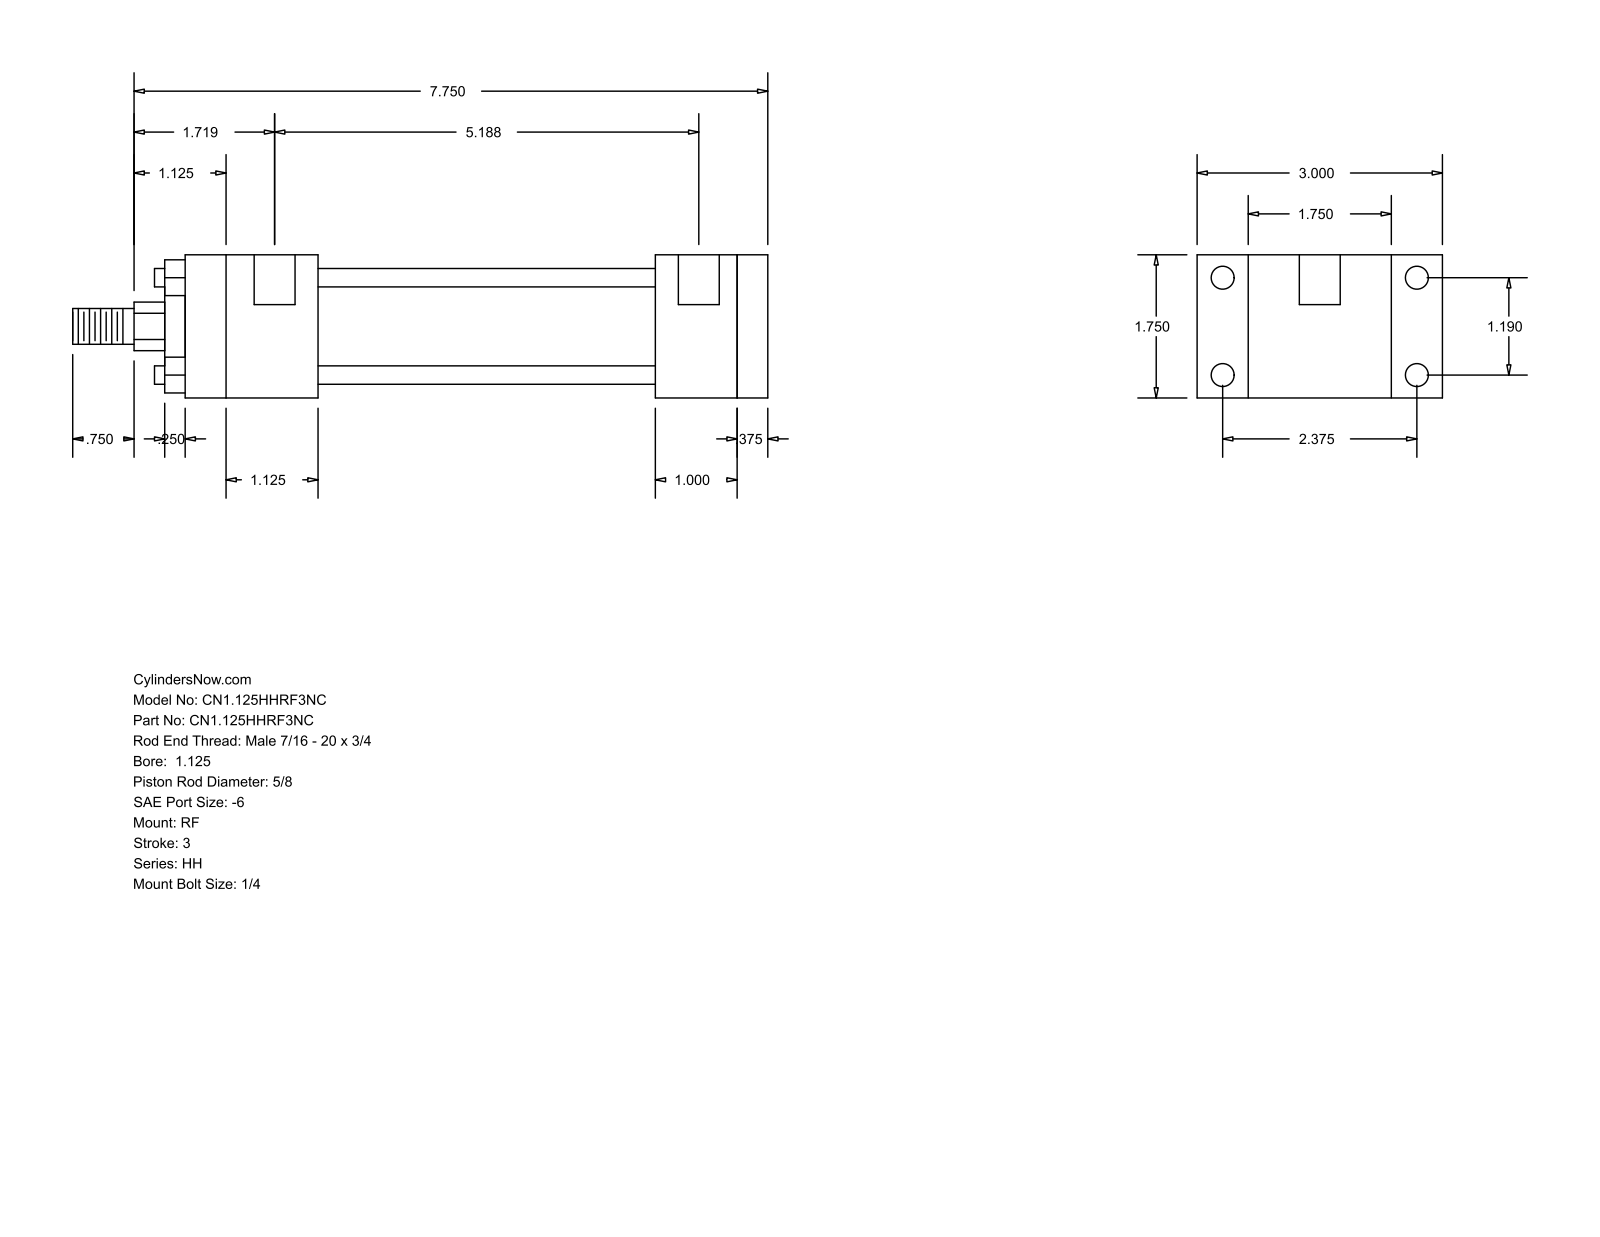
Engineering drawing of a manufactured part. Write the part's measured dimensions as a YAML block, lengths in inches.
part_name: "HH_RF__0112_0.625"
step_written_by: "GSSL Pune (CONFIG_CONTROL_DESIGN)"
units: inches
bodies: {solids: 0, faces: 92, planar: 64, cylindrical: 28, other: 0}
overall_size: [8.5, 3, 1.75]
round_holes:
  - {diameter: 0.219, count: 4}
  - {diameter: 0.281, count: 4}
  - {diameter: 0.5, count: 2}
round_bosses_or_shafts:
  - {diameter: 0.225, count: 4}
  - {diameter: 1.375, count: 1}
  - {diameter: 1.125, count: 1}
  - {diameter: 0.625, count: 1}
  - {diameter: 0.437, count: 1}
partial_cylinders:
  - {radius: 0.297, count: 1}
face_to_face_distances: [1.75, 0.375, 7.125, 0.625, 5.125, 5.5, 4.125, 1, 1.375, 1.625]
hole_center_spacings: [1.19, 2.375, 2.656, 5.063, 0.125, 5.187]
